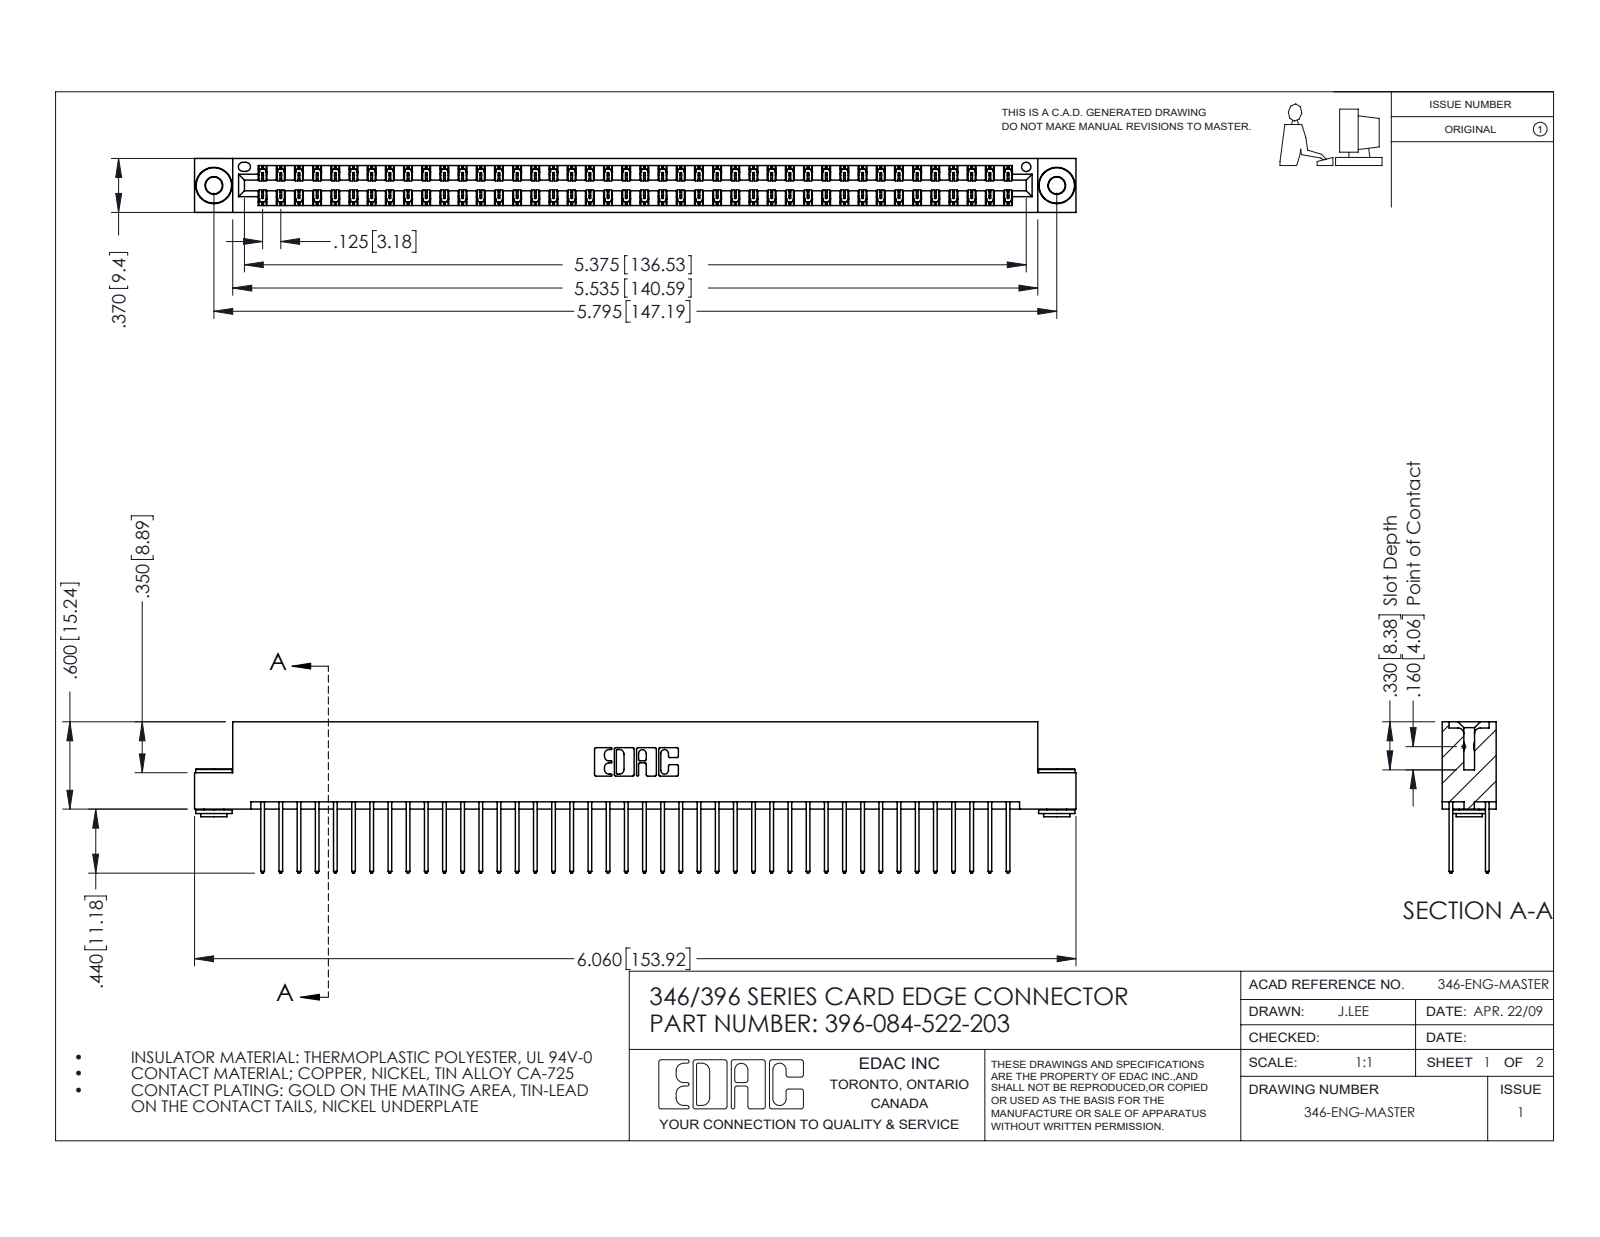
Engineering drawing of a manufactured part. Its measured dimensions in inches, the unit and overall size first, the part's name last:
Units: inches
Overall size (bounding box): 6.06 × 1.04 × 0.37
Round holes (diameter × count): ⌀0.116 ×2, ⌀0.156 ×2, ⌀0.064 ×1
Round bosses / shafts (diameter × count): ⌀0.25 ×2, ⌀0.18 ×2, ⌀0.136 ×2
Partial cylindrical surfaces — rounded edges, fillets, slot ends (radius × count): R0.006 ×126, R0.01 ×84, R0.01 ×22, R0.007 ×6, R0.031 ×6, R0.026 ×3, R0.014 ×2, R0.022 ×2
Main face-to-face distances: 0.048, 0.322, 0.25, 0.025, 0.37, 0.072, 0.298, 0.275, 0.148, 0.222
Hole centre spacings: 0.246, 5.586, 5.795
Volume: 0.93 in³ · Surface area: 34.36 in²
Bodies: 87 solids, 4528 faces (3026 planar, 1494 cylindrical, 8 other)
Part name (STEP PRODUCT): 396-084-522-203; 345-250-002_345-250-002-102; 346 Part_Flush Mounting Lugs - 0.156 Dia-TH; 345-292-001_345-293-122
STEP written by: SolidWorks 2016 (CONFIG_CONTROL_DESIGN)
